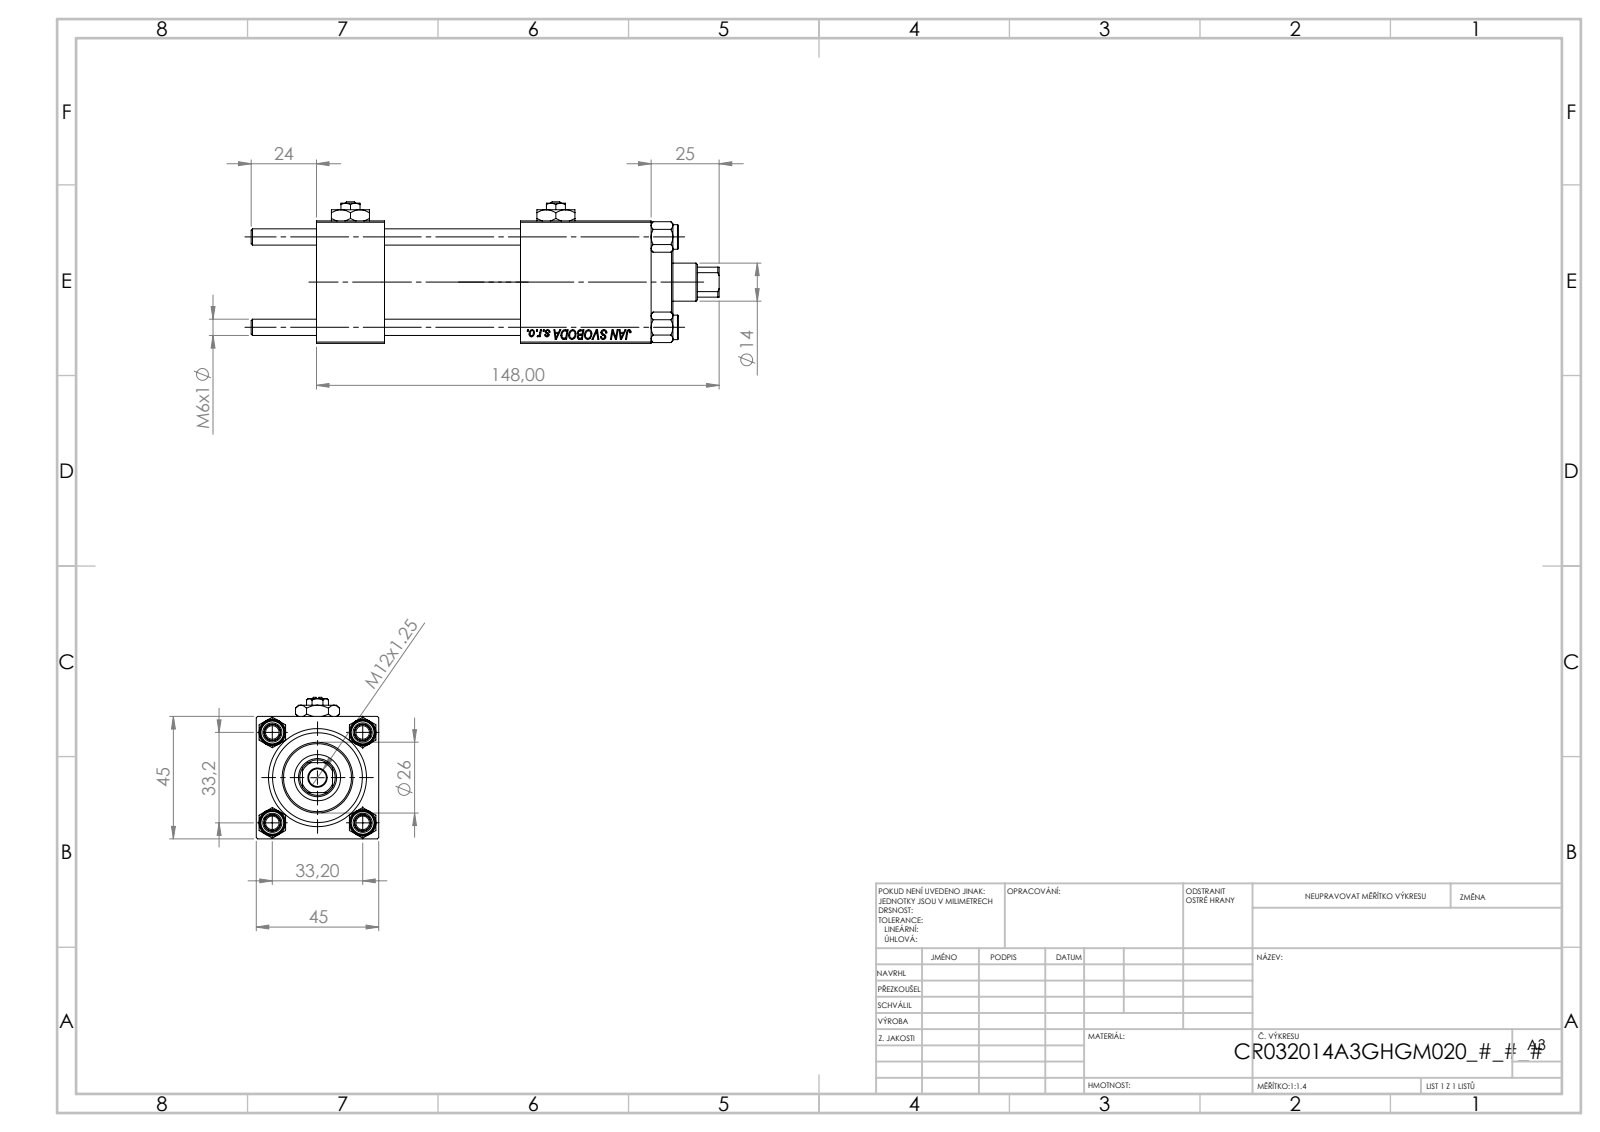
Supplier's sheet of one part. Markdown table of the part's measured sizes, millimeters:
| quantity | value |
| --- | --- |
| part name | NUT_M5; V215_VC_A; Zatka_pro_OIL_PORT; V215CR_BODY_A (+2 more) |
| STEP written by | SolidWorks 2019 (CONFIG_CONTROL_DESIGN) |
| units | millimeters |
| bodies | 13 solids, 1232 faces (566 planar, 88 cylindrical, 578 other) |
| overall size | 172 × 52 × 45 |
| volume | 196 758 mm³ |
| surface area | 74 664 mm² |
| round holes (diameter × count) | 6 × 4, 7 × 2, 13.16 × 2, 20 × 2, 6.5 × 1, 14 × 1, 17 × 1, 24 × 1, 32 × 1, 33 × 1 |
| round bosses / shafts (diameter × count) | 9 × 4, 38 × 1, 26 × 1 |
| partial cylindrical surfaces (radius × count) | 6.5 × 1 |
| main face-to-face distances | 45, 25, 123, 98, 50, 75, 48, 94.3, 69.3, 19.3 |
| hole center spacings | 23.48, 33.2, 46.95, 75.5 |
